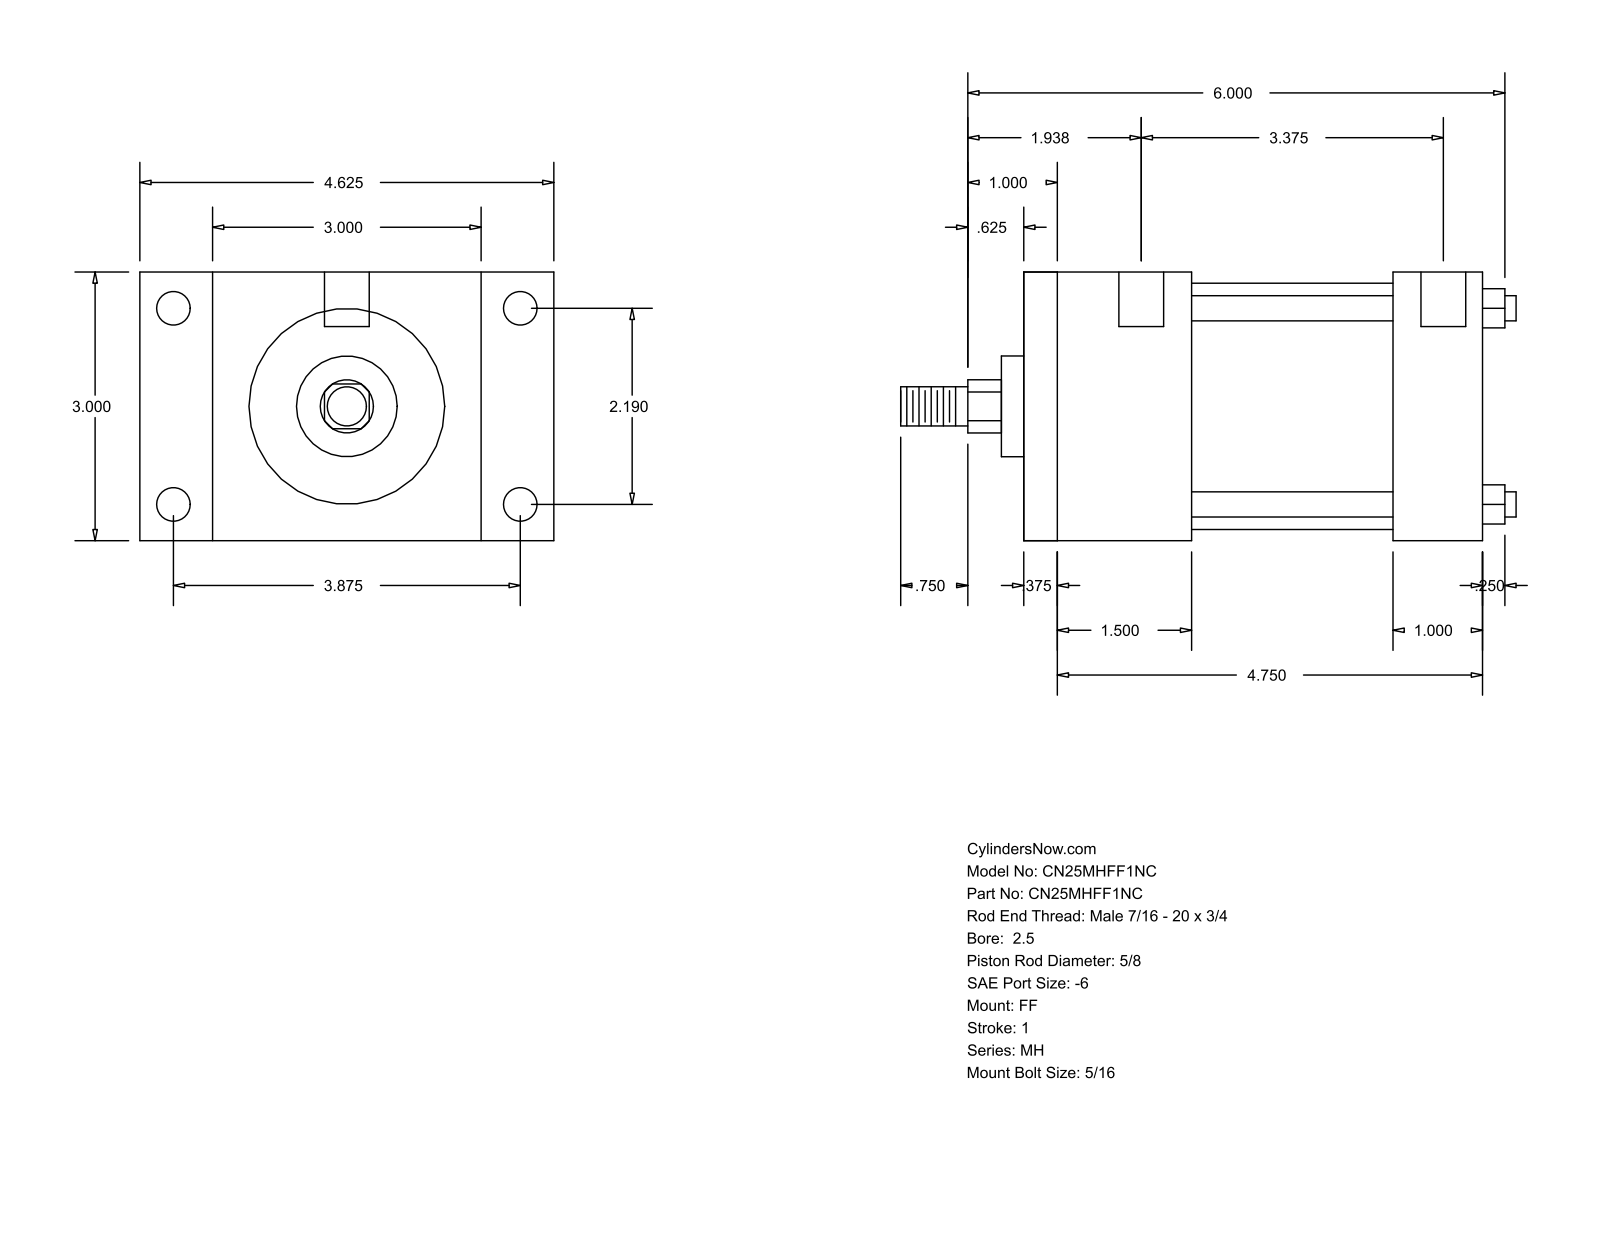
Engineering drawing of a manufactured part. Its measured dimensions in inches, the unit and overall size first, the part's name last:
Units: inches
Overall size (bounding box): 6.875 × 4.625 × 3
Round holes (diameter × count): ⌀0.219 ×4, ⌀0.375 ×4, ⌀0.5 ×2
Round bosses / shafts (diameter × count): ⌀0.281 ×4, ⌀2.75 ×1, ⌀1.125 ×1, ⌀0.625 ×1, ⌀0.437 ×1
Partial cylindrical surfaces — rounded edges, fillets, slot ends (radius × count): R0.297 ×1
Main face-to-face distances: 3, 5.125, 0.375, 4.75, 1, 3.25, 2.25, 1.875, 4.125, 1.5
Hole centre spacings: 2.19, 3.687, 3.875, 4.451, 0.125, 0.187, 3.375, 3.5
Bodies: 0 solids, 92 faces (64 planar, 28 cylindrical, 0 other)
Part name (STEP PRODUCT): MH_FF__0250_0.625
STEP written by: GSSL Pune (CONFIG_CONTROL_DESIGN)
